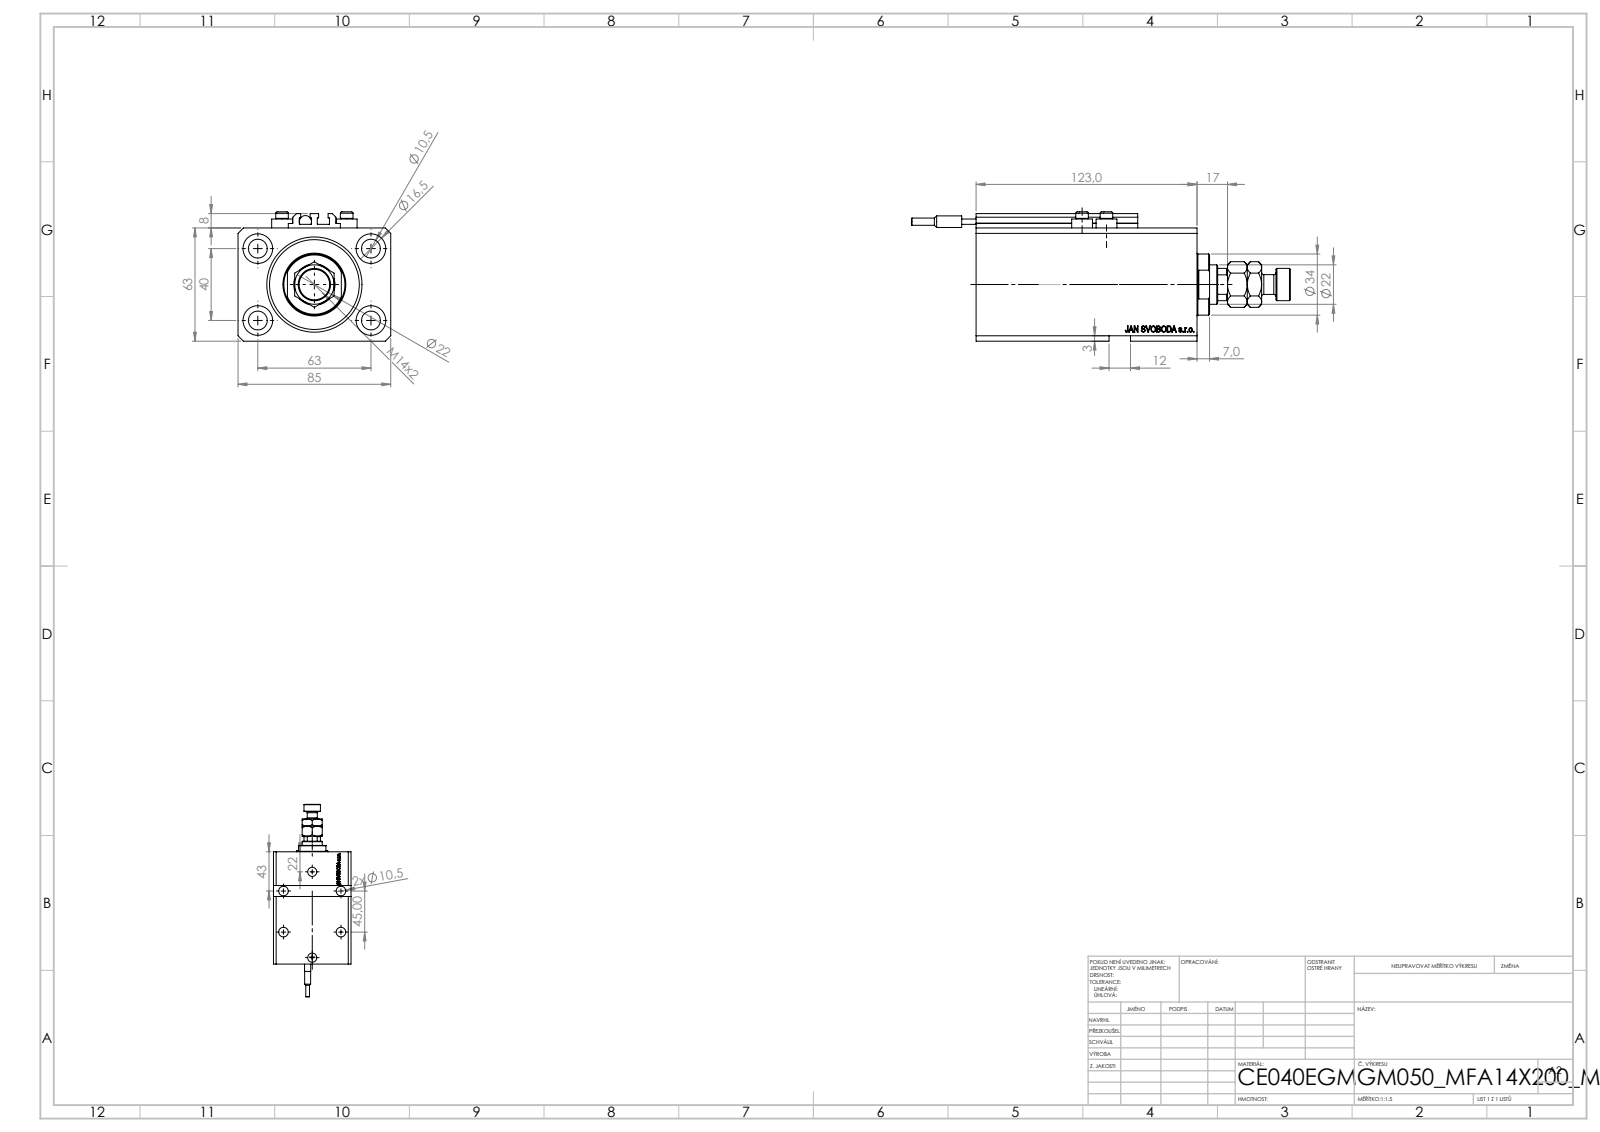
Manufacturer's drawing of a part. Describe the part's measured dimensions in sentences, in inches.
The part is named "MFA; V250CE_C_VCP; V250CE_E_Body; ALLEN BOLT V250CE (+2 more)". Its 3-D file was written by "SolidWorks 2019 (CONFIG_CONTROL_DESIGN)". It is 10 solids with 1185 faces: 567 planar, 156 cylindrical and 462 other. Overall it measures 8.307 by 3.346 by 2.835 inches. Its volume is 34.73 cubic inches and its surface area 192.1 square inches. Round holes: 8 of diameter 0.413, 4 of diameter 0.049, 4 of diameter 0.157, 4 of diameter 0.65, 2 of diameter 0.394, 2 of diameter 0.518, 2 of diameter 0.787, 1 of diameter 0.492, 1 of diameter 0.866, 1 of diameter 1.575, 1 of diameter 2.087. Round bosses or shafts: 4 of diameter 0.457, 4 of diameter 0.276, 1 of diameter 1.339, 1 of diameter 0.709, 1 of diameter 0.433, 1 of diameter 0.268, 1 of diameter 0.256, 1 of diameter 0.157. Partial cylindrical surfaces (rounded edges, fillets, slot ends): 10 of radius 0.008, 1 of radius 0.413. The main face-to-face distances are 2.48, 3.346, 0.669, 4.843, 4.173, 0.449, 3.724, 4.394, 0.118, 2.559. The hole center spacings are 1.469, 2.48, 0.535, 0.606, 0.983, 1.084, 1.324, 1.417.
